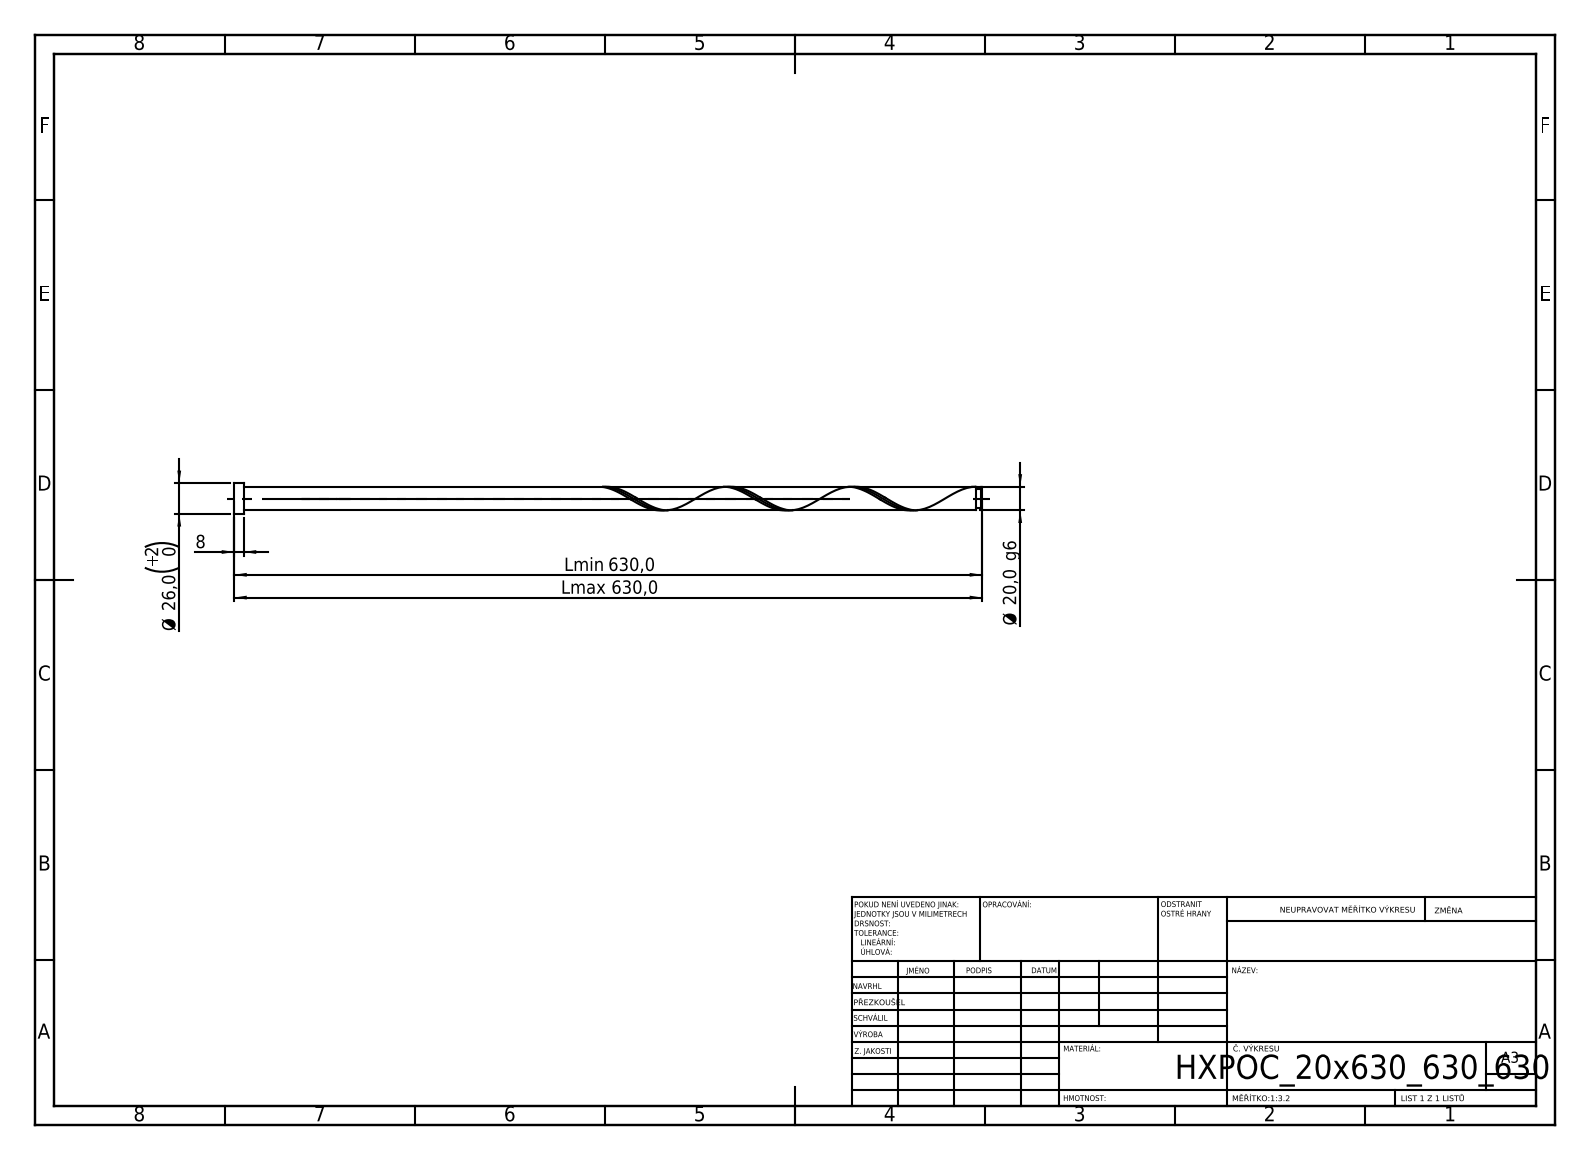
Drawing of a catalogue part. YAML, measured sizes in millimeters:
step_written_by: "SolidWorks 2019 (CONFIG_CONTROL_DESIGN)"
units: millimeters
bodies: {solids: 1, faces: 21, planar: 6, cylindrical: 14, other: 1}
overall_size: [630, 26, 26]
volume: 197307
surface_area: 41710
round_bosses_or_shafts:
  - {diameter: 26, count: 1}
  - {diameter: 20, count: 1}
  - {diameter: 16, count: 1}
face_to_face_distances: [630, 8, 622, 628.92, 620.92, 1.08, 624.92, 616.92, 4, 5.08]
